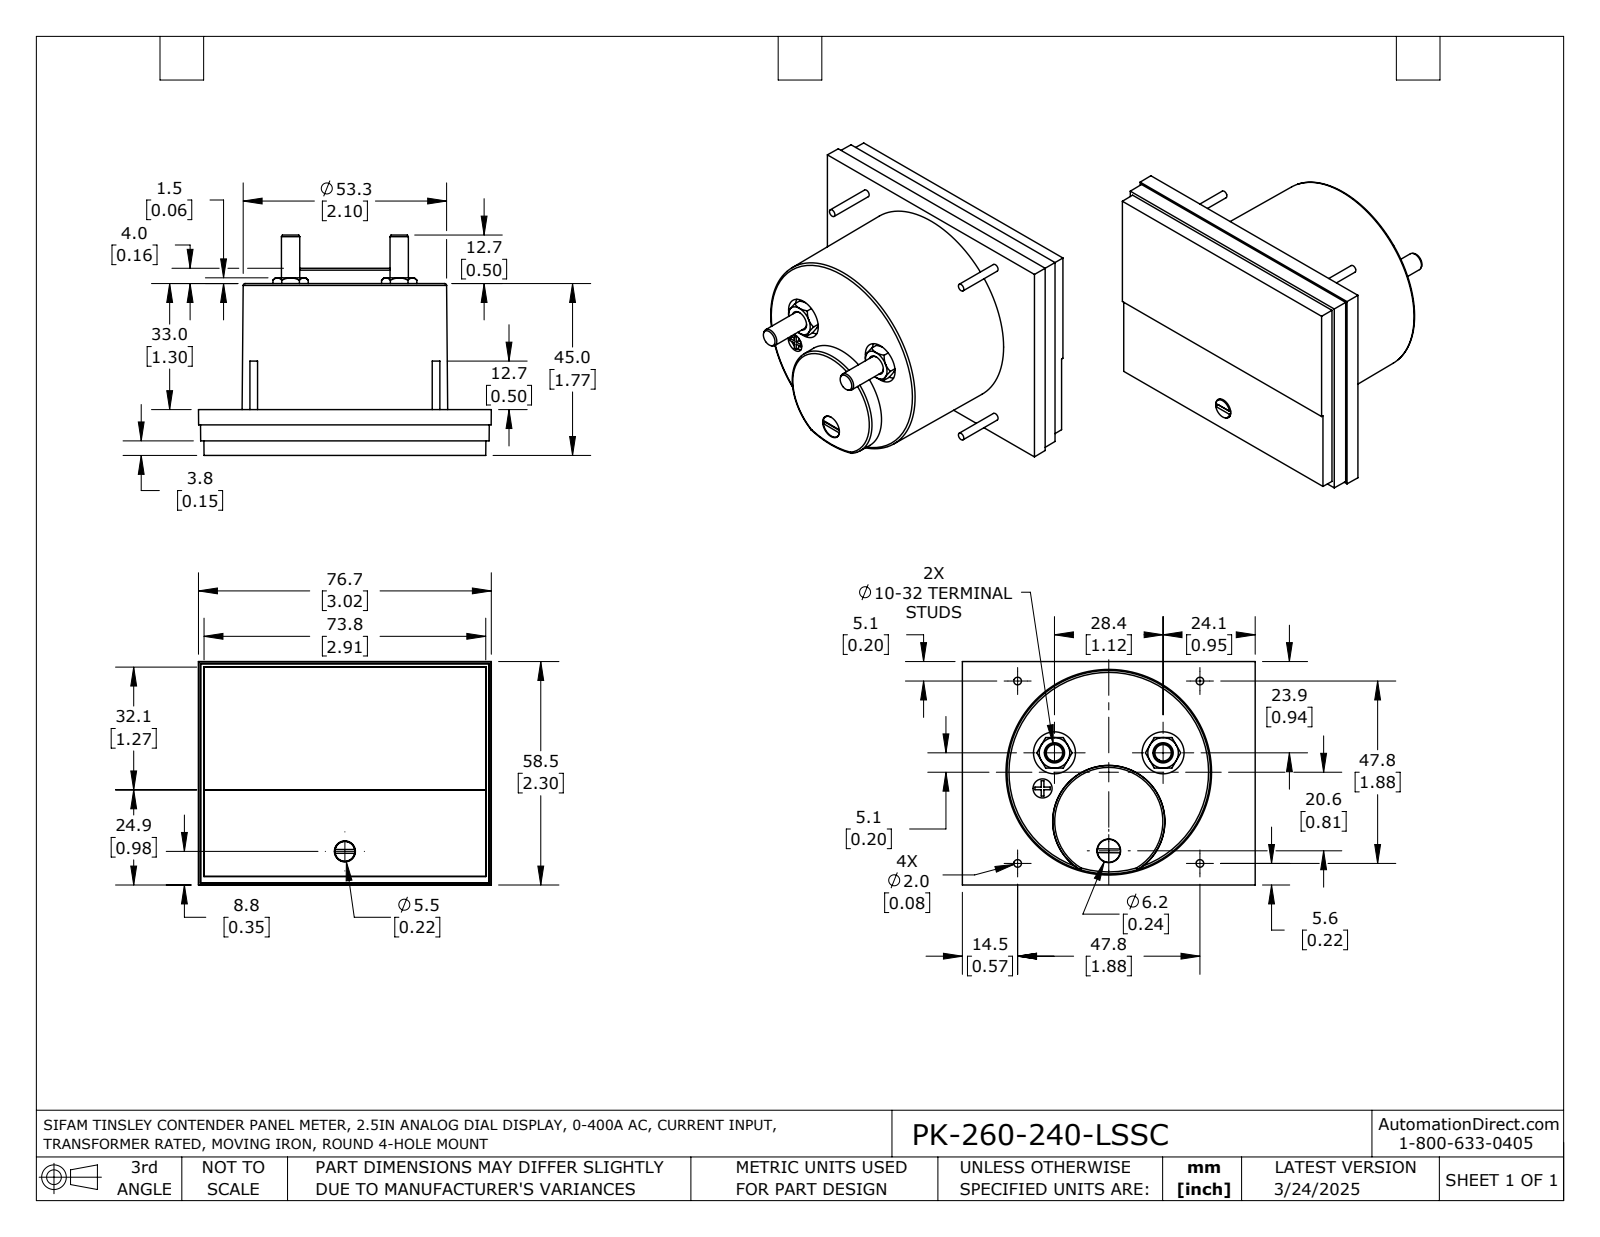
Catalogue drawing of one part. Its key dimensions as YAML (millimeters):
part_name: "PK-260-240-LSSC"
step_written_by: "SolidWorks 2021 (AUTOMOTIVE_DESIGN)"
units: millimeters
bodies: {solids: 1, faces: 192, planar: 95, cylindrical: 37, other: 60}
overall_size: [76.7, 58.5, 57.7]
volume: 125500
surface_area: 23580
round_holes:
  - {diameter: 5, count: 3}
  - {diameter: 11, count: 2}
  - {diameter: 5.3, count: 1}
  - {diameter: 5.5, count: 1}
  - {diameter: 6.2, count: 1}
round_bosses_or_shafts:
  - {diameter: 2, count: 4}
  - {diameter: 4.8, count: 2}
  - {diameter: 6, count: 1}
  - {diameter: 5.2, count: 1}
partial_cylinders:
  - {radius: 0.8, count: 1}
face_to_face_distances: [0.5, 12, 3.3, 8.2, 3.8, 11.5, 1.4, 2, 10.1, 1.9]
hole_center_spacings: [29.3, 29.5, 9.8, 23.8, 23.9, 28.4, 32.9]
